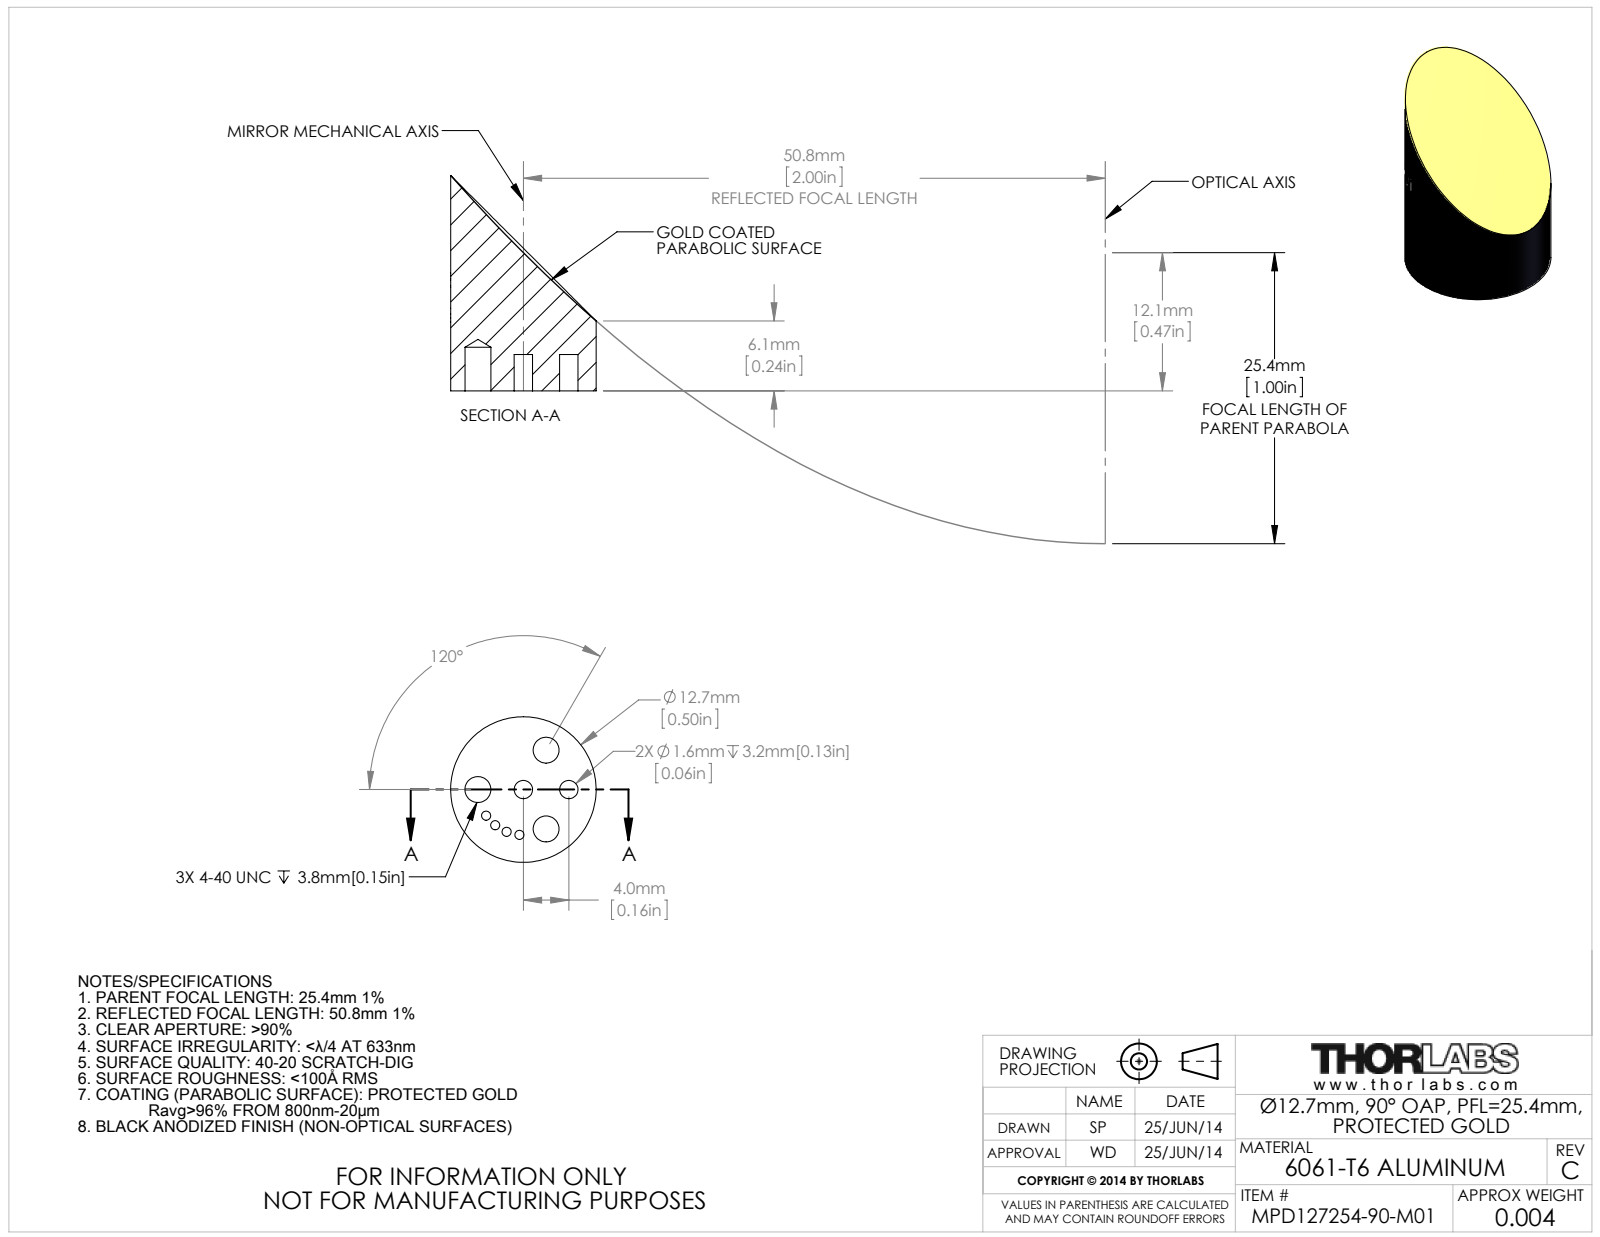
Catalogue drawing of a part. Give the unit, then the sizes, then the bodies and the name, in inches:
Units: inches
Overall size (bounding box): 0.74 × 0.5 × 0.5
Round holes (diameter × count): ⌀0.089 ×3, ⌀0.063 ×2
Round bosses / shafts (diameter × count): ⌀0.5 ×1
Main face-to-face distances: 0.125
Hole centre spacings: 0.156, 0.27, 0.271, 0.313
Volume: 0.091 in³ · Surface area: 1.424 in²
Bodies: 1 solid, 66 faces (3 planar, 47 cylindrical, 16 other)
Part name (STEP PRODUCT): 21172-E0W
STEP written by: SolidWorks 2014 (CONFIG_CONTROL_DESIGN)
